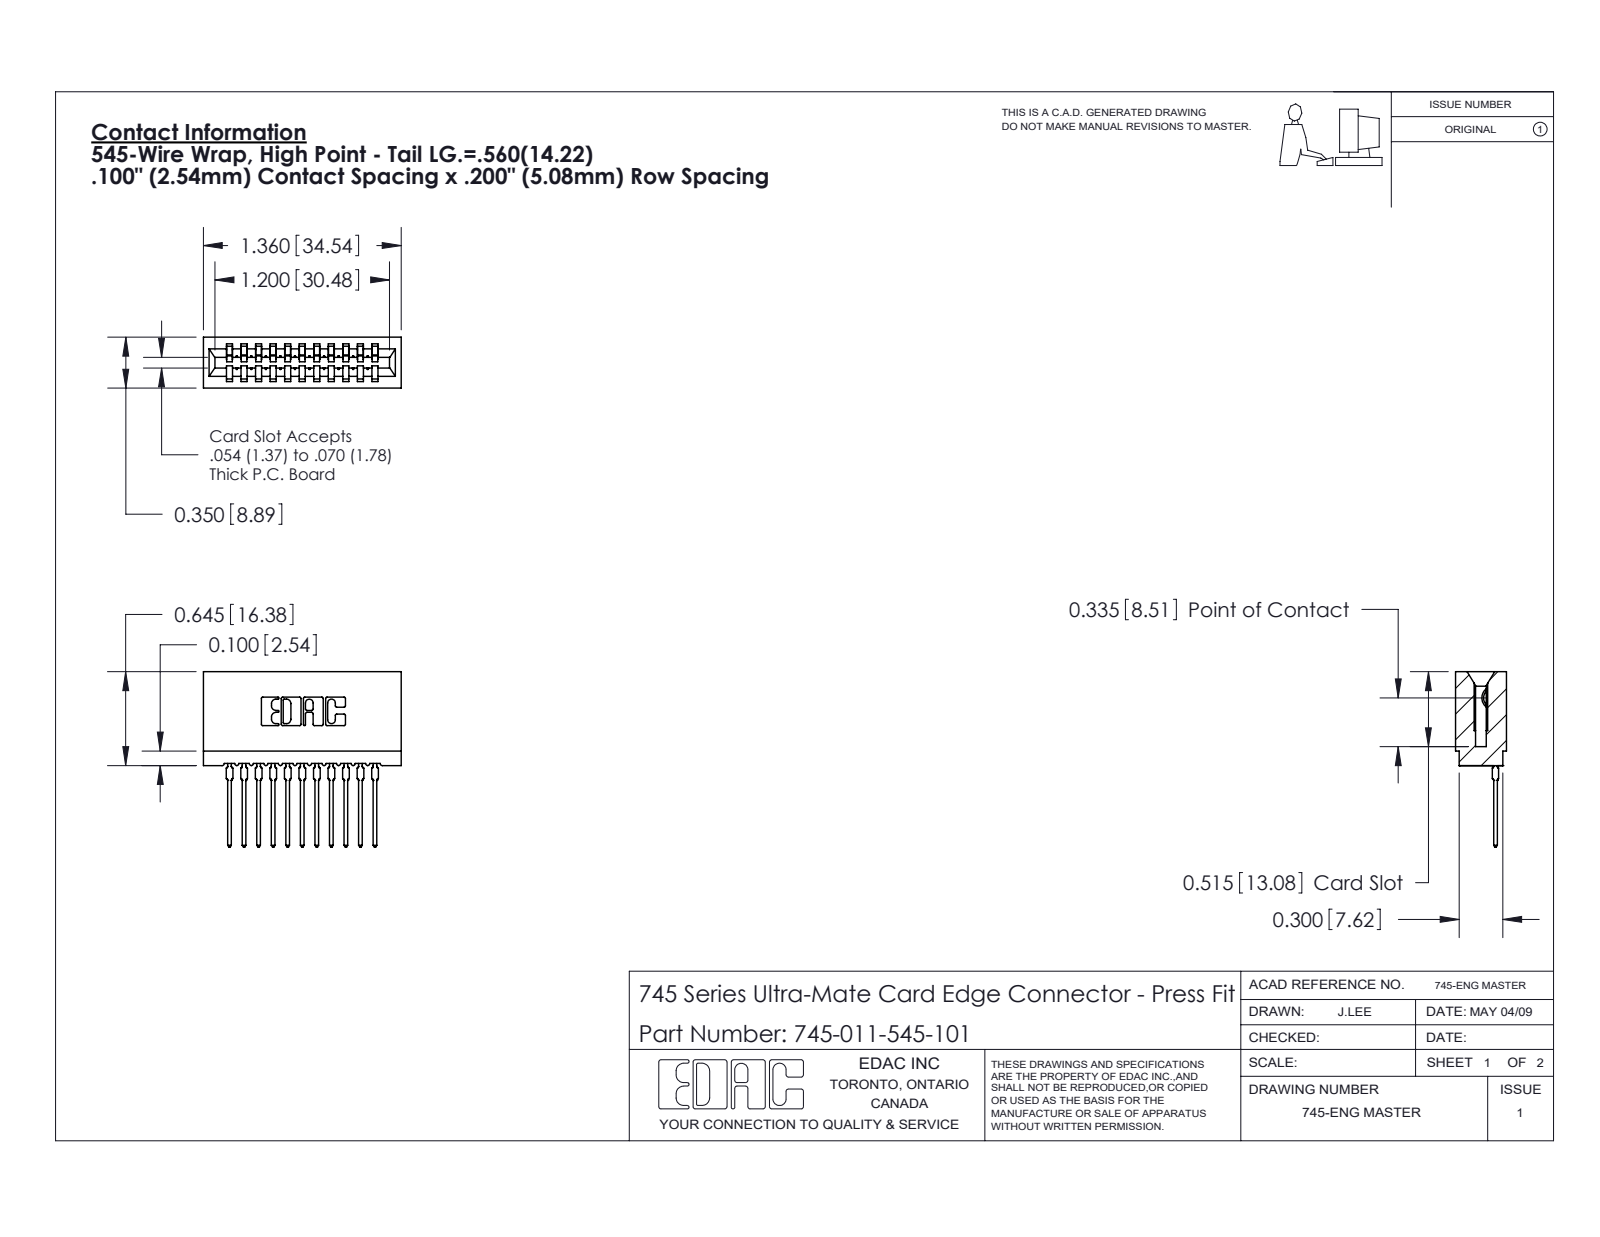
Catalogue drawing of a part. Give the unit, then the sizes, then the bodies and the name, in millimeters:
Units: millimetres
Overall size (bounding box): 34.5 × 30.6 × 8.9
Partial cylindrical surfaces — rounded edges, fillets, slot ends (radius × count): R0.3 ×22, R0.4 ×22, R0.5 ×22, R0.2 ×6, R0.8 ×6, R0.1 ×4, R0.3 ×4, R0.7 ×3
Main face-to-face distances: 2.5, 5.1, 7.6, 10.2, 12.7, 11.2, 8.7, 6.1, 3.6, 1.1
Volume: 3 230 mm³ · Surface area: 5 568 mm²
Bodies: 12 solids, 1327 faces (792 planar, 249 cylindrical, 286 other)
Part name (STEP PRODUCT): 745-292-001_545; 745-011-545-101; 745 Part_Insulator Option - 01
STEP written by: SolidWorks 2020 (CONFIG_CONTROL_DESIGN)
